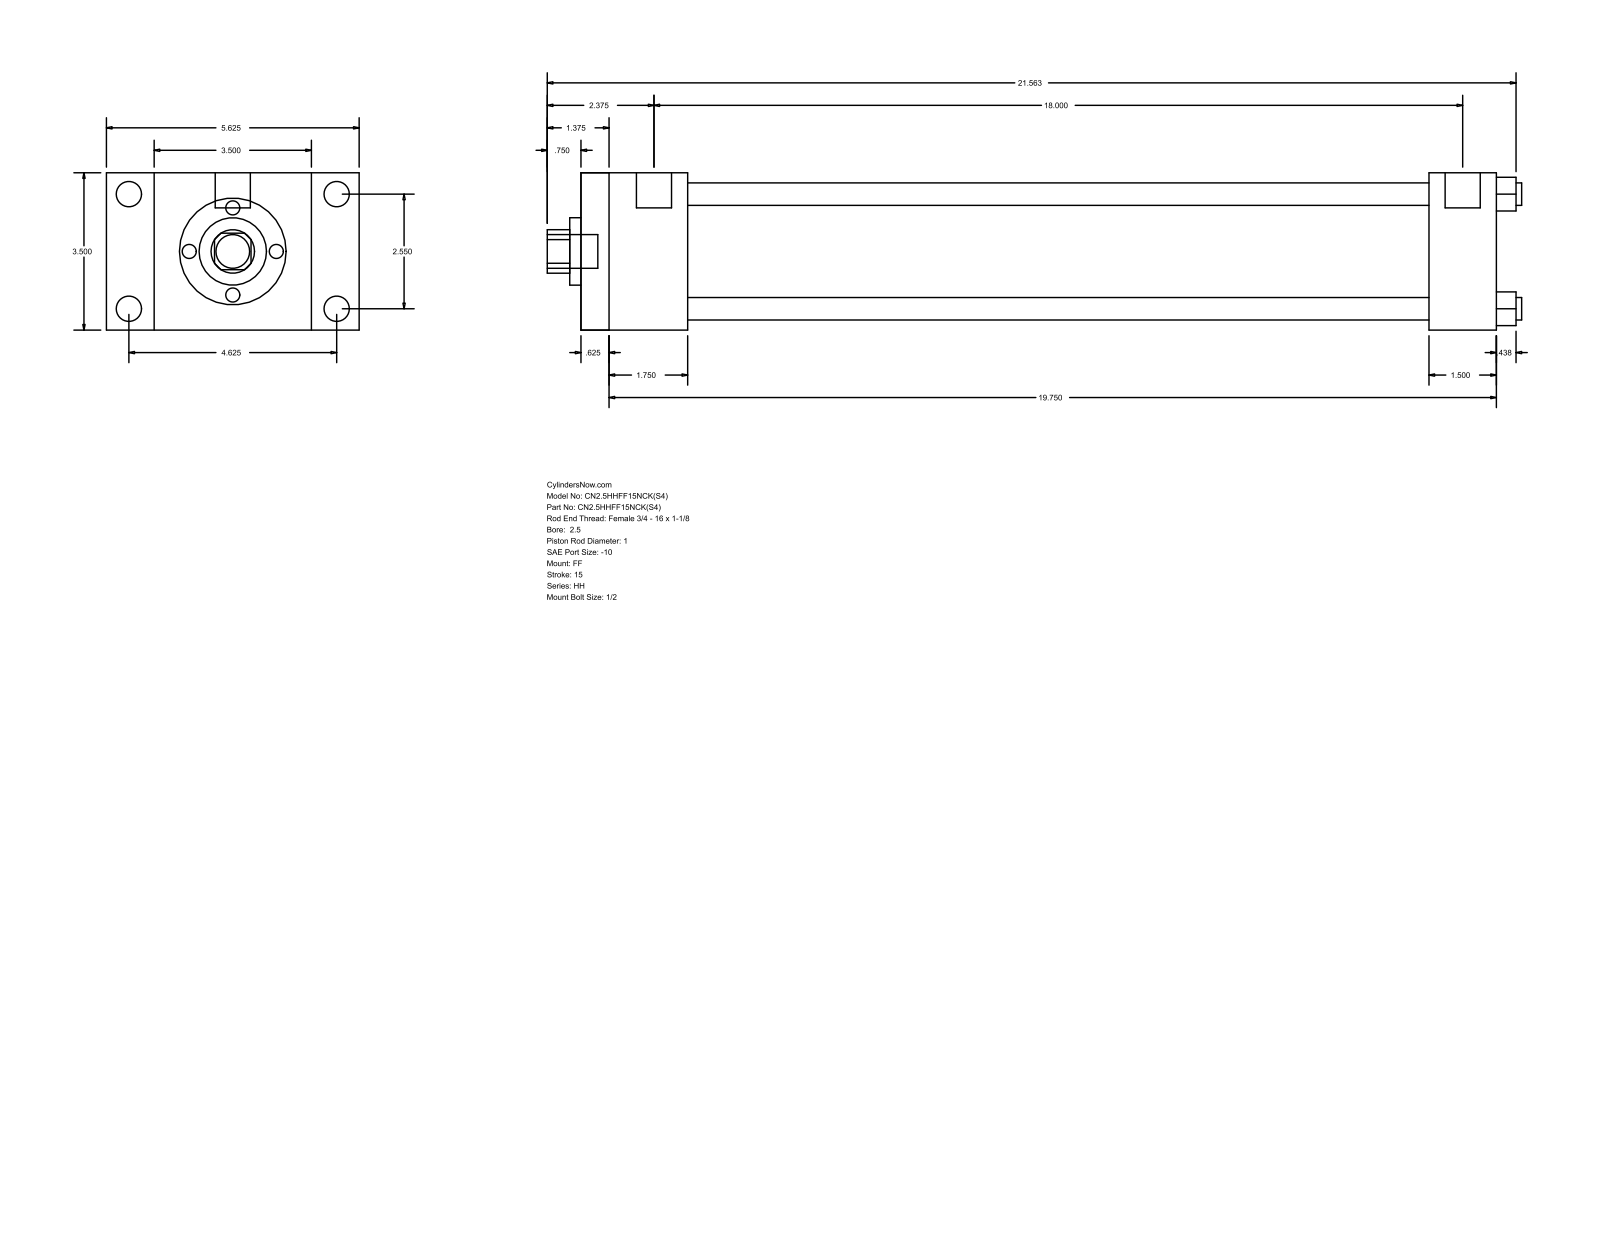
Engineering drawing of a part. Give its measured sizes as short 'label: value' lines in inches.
name: HH_FF__0250_1
written by: GSSL Pune (CONFIG_CONTROL_DESIGN)
unit: in
bodies: 0 solids, 92 faces (64 planar, 28 cylindrical, 0 other)
size: 21.687 × 5.625 × 3.5
holes: 4× ⌀0.5, 1× ⌀1, 1× ⌀1.5, 1× ⌀2.875
bosses: 4× ⌀0.563, 4× ⌀0.219, 2× ⌀0.781, 1× ⌀0.75
rounds: 1× R0.484
face distances: 3.5, 20.375, 0.625, 19.75, 2.375, 1.75, 18, 18.875, 18.25, 16.5
hole spacings: 1.803, 2.55, 3.606
